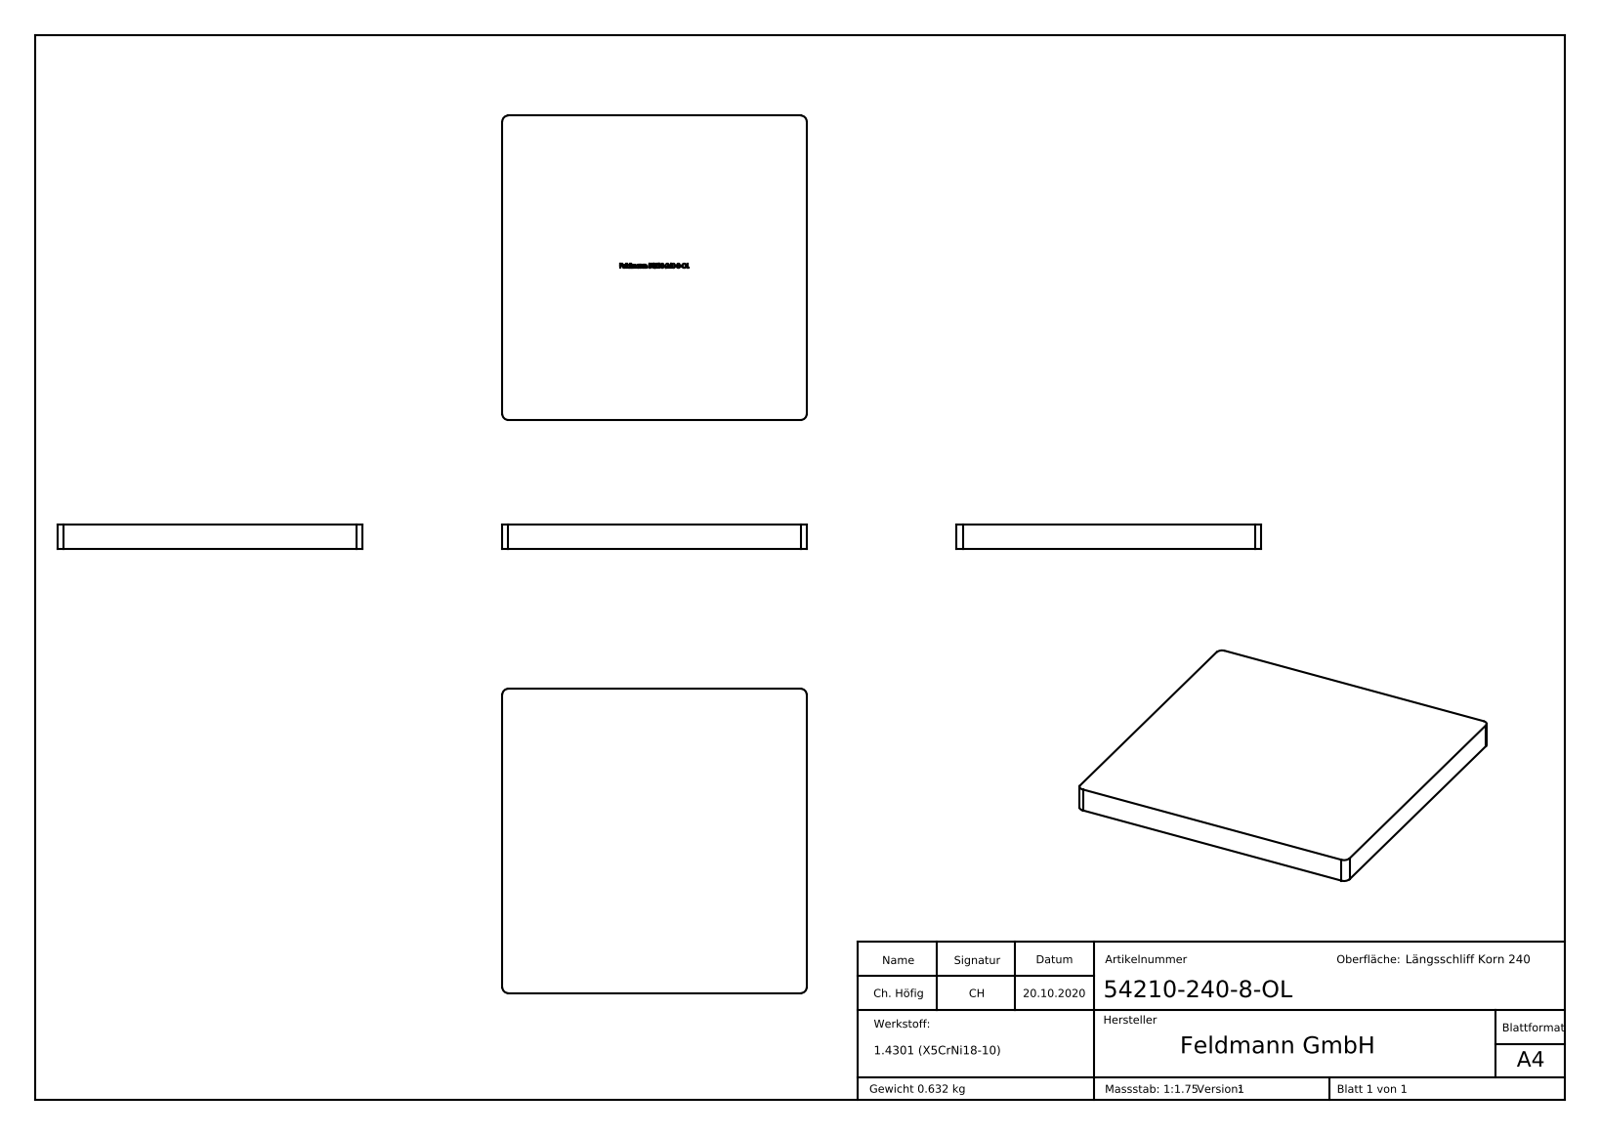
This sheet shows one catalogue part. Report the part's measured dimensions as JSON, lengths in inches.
{"part_name": "54210-240-8-OL", "step_written_by": "SolidWorks 2018 (CONFIG_CONTROL_DESIGN)", "units": "inches", "bodies": {"solids": 1, "faces": 275, "planar": 160, "cylindrical": 4, "other": 111}, "overall_size": [3.937, 3.937, 0.315], "volume_in3": 4.88, "surface_area_in2": 35.92, "partial_cylinders_radius": [[0.079, 4]], "face_to_face_distances": [0.315, 3.937, 0.311, 1.969, 0.017, 0.035, 0.023, 1.986, 1.951, 1.956]}
